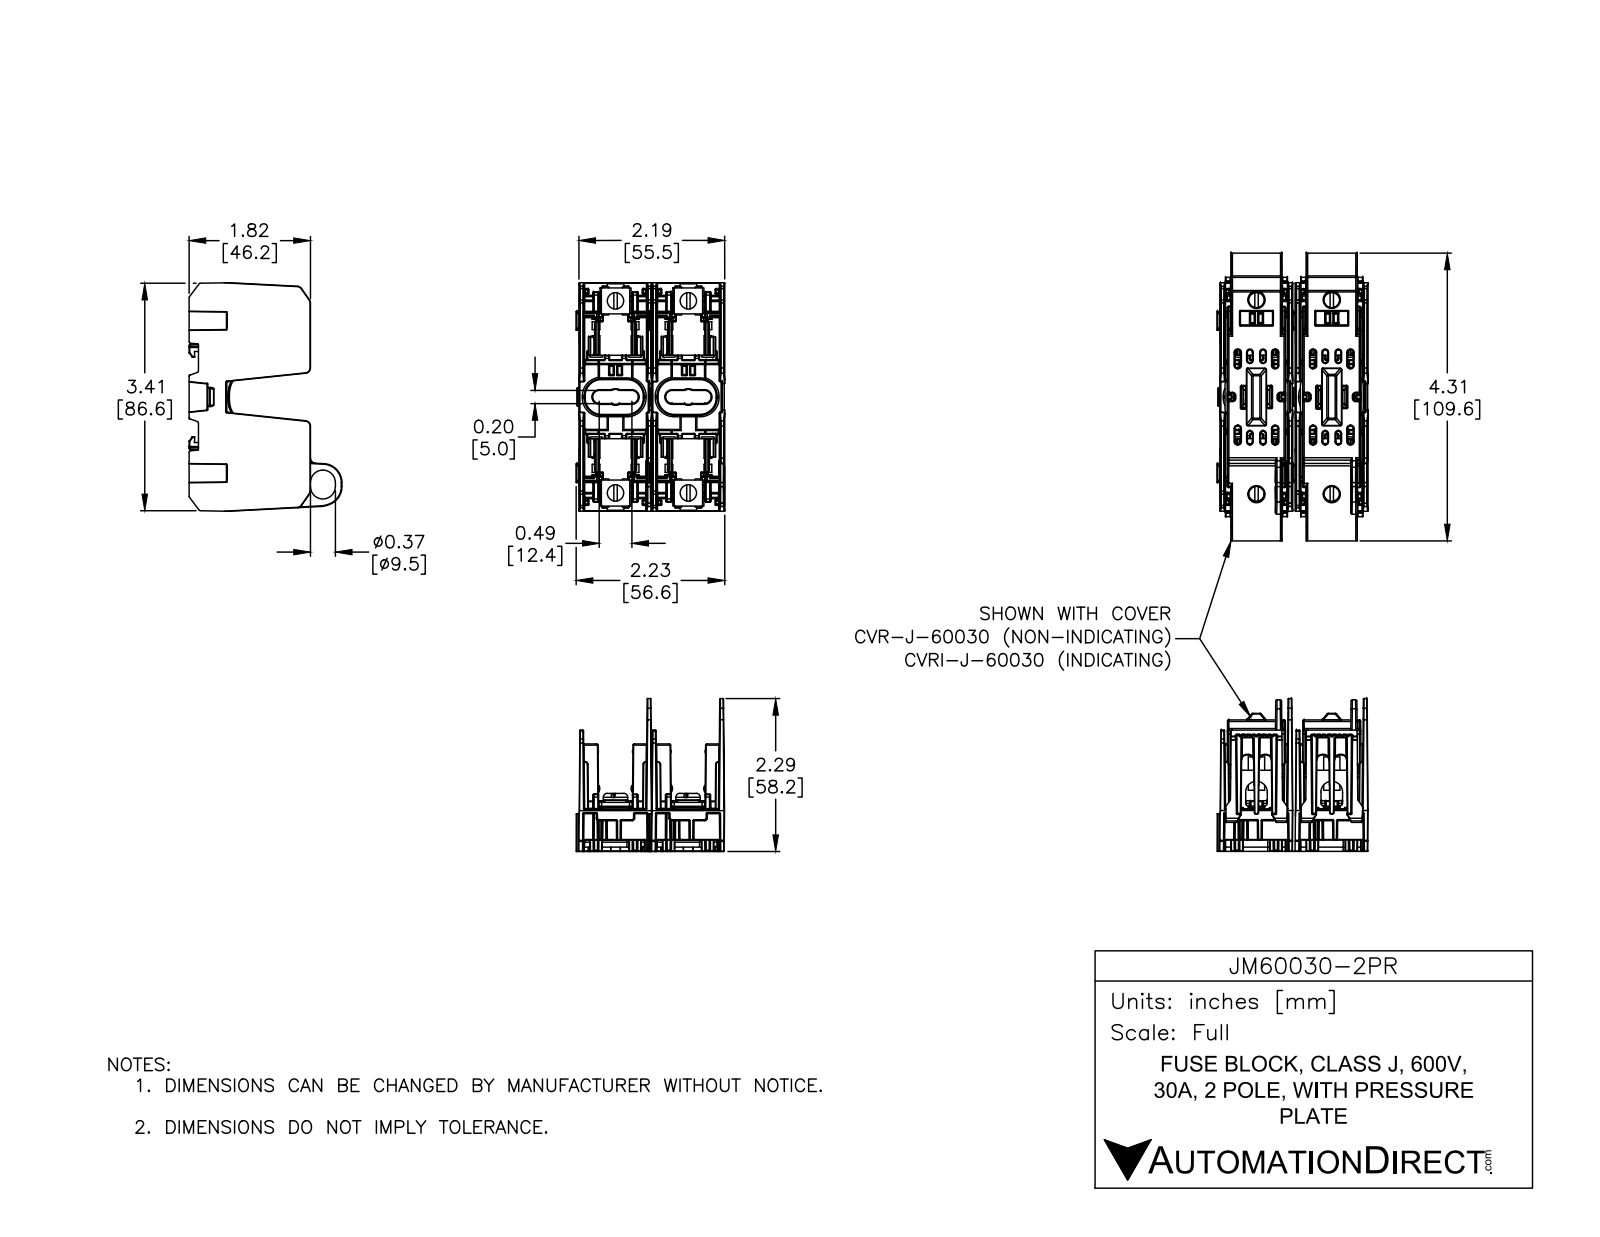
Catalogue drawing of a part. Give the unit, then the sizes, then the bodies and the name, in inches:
Units: inches
Overall size (bounding box): 3.433 × 2.291 × 2.223
Round holes (diameter × count): ⌀0.225 ×4, ⌀0.244 ×4
Round bosses / shafts (diameter × count): ⌀0.244 ×4
Partial cylindrical surfaces — rounded edges, fillets, slot ends (radius × count): R0.01 ×760, R0.006 ×591, R0.02 ×87, R0.039 ×60, R0.004 ×48, R0.02 ×16, R0.059 ×12, R0.079 ×11
Main face-to-face distances: 1.089, 1.013, 0.024, 1.014, 0.075, 2.102, 0.076, 1.089, 2.103, 0.065
Hole centre spacings: 1.089, 1.241, 0.595, 0.595, 1.689, 2.01, 2.284, 2.285
Volume: 3.951 in³ · Surface area: 103.2 in²
Bodies: 26 solids, 6186 faces (1562 planar, 2658 cylindrical, 1966 other)
Part name (STEP PRODUCT): JM60030-2PR; JM60030-1CR
STEP written by: SolidWorks 2016 (AUTOMOTIVE_DESIGN)
